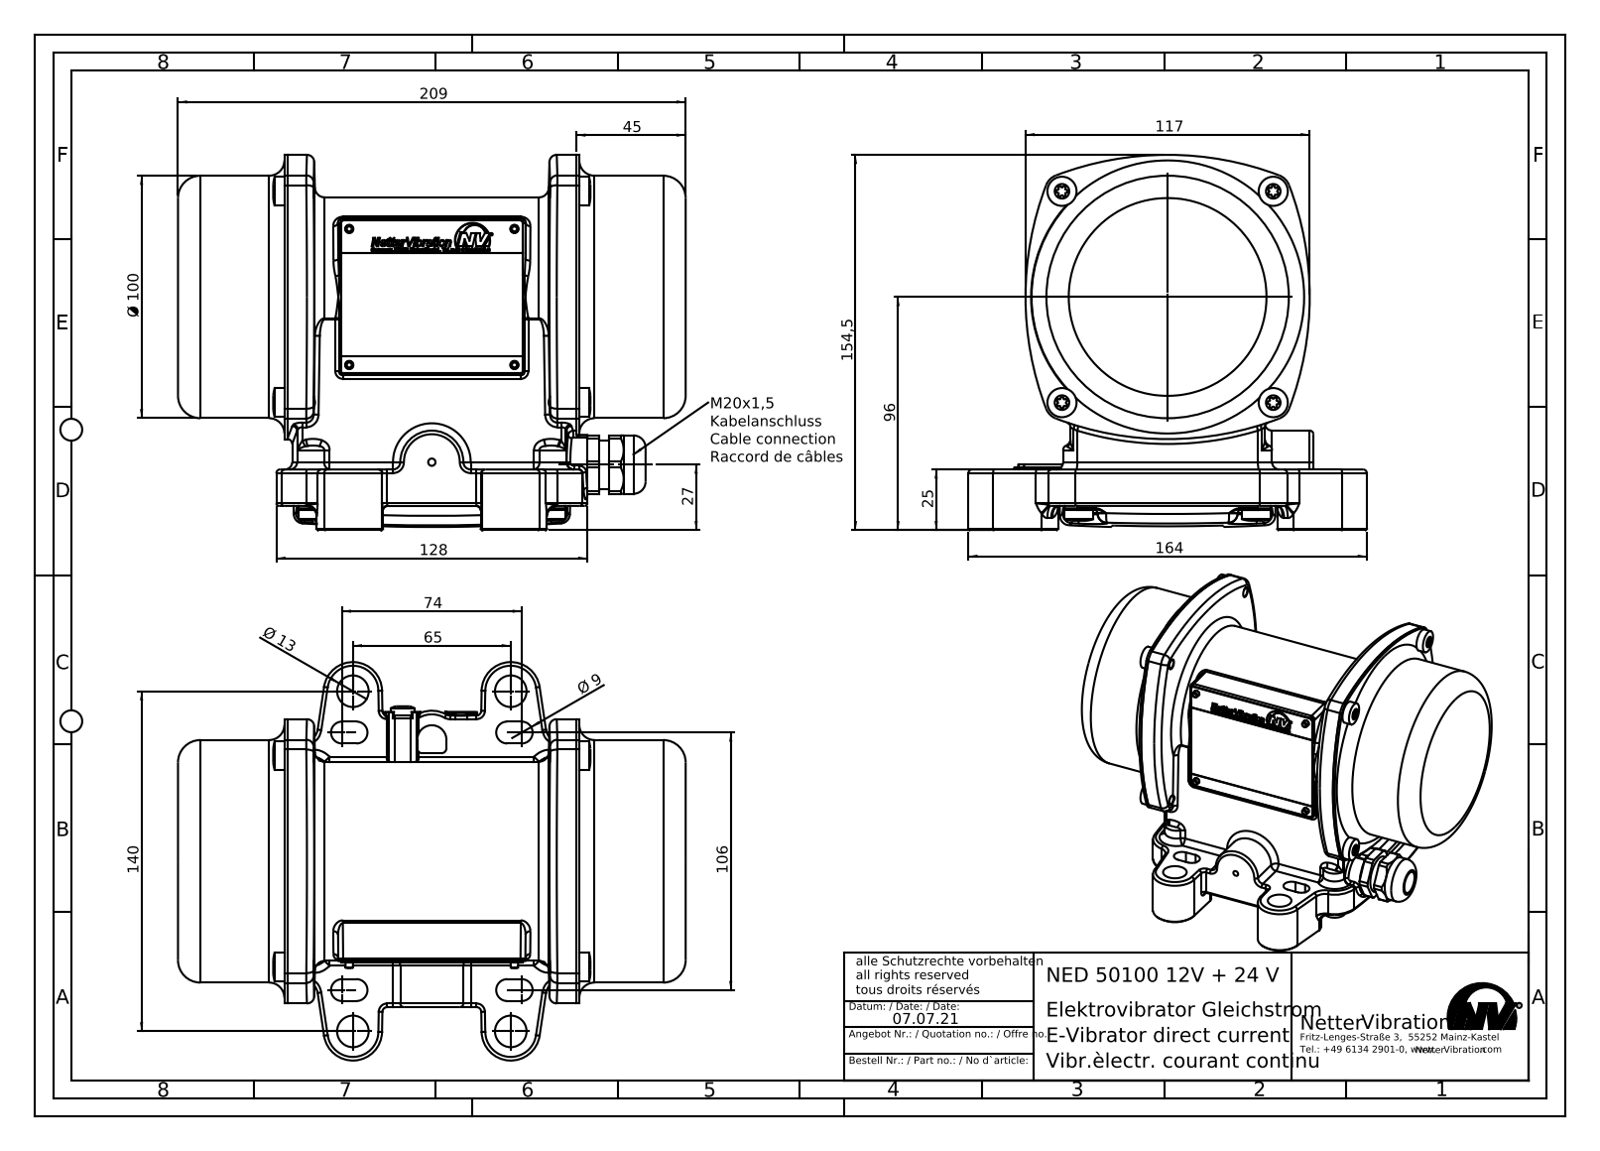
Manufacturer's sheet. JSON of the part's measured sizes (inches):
{"part_name": "NED 50100 12V+24V", "step_written_by": "SolidWorks 2015 (AUTOMOTIVE_DESIGN)", "units": "inches", "bodies": {"solids": 64, "faces": 7209, "planar": 1770, "cylindrical": 1792, "other": 3647}, "overall_size": [8.228, 6.457, 6.083], "volume_in3": 82.02, "surface_area_in2": 824.6, "round_holes": [[0.26, 10], [0.13, 6], [0.134, 4], [0.276, 4], [0.394, 3], [0.098, 2], [0.512, 2], [0.413, 1], [0.453, 1], [0.472, 1], [0.571, 1], [0.591, 1]], "round_bosses_or_shafts": [[0.236, 18], [0.472, 8], [0.276, 6], [0.157, 6], [0.197, 3], [0.787, 2], [0.551, 2], [0.394, 2]], "partial_cylinders_radius": [[0.02, 133], [0.012, 101], [0.008, 59], [0.059, 59], [0.079, 42], [0.236, 27], [0.039, 26], [0.118, 22]], "face_to_face_distances": [0.157, 6.358, 0.047, 0.315, 6.516, 6.201, 1.724, 6.457, 0.809, 0.856], "hole_center_spacings": [1.575, 0.501, 0.547, 0.709, 1.077, 1.002, 1.12, 1.718]}
